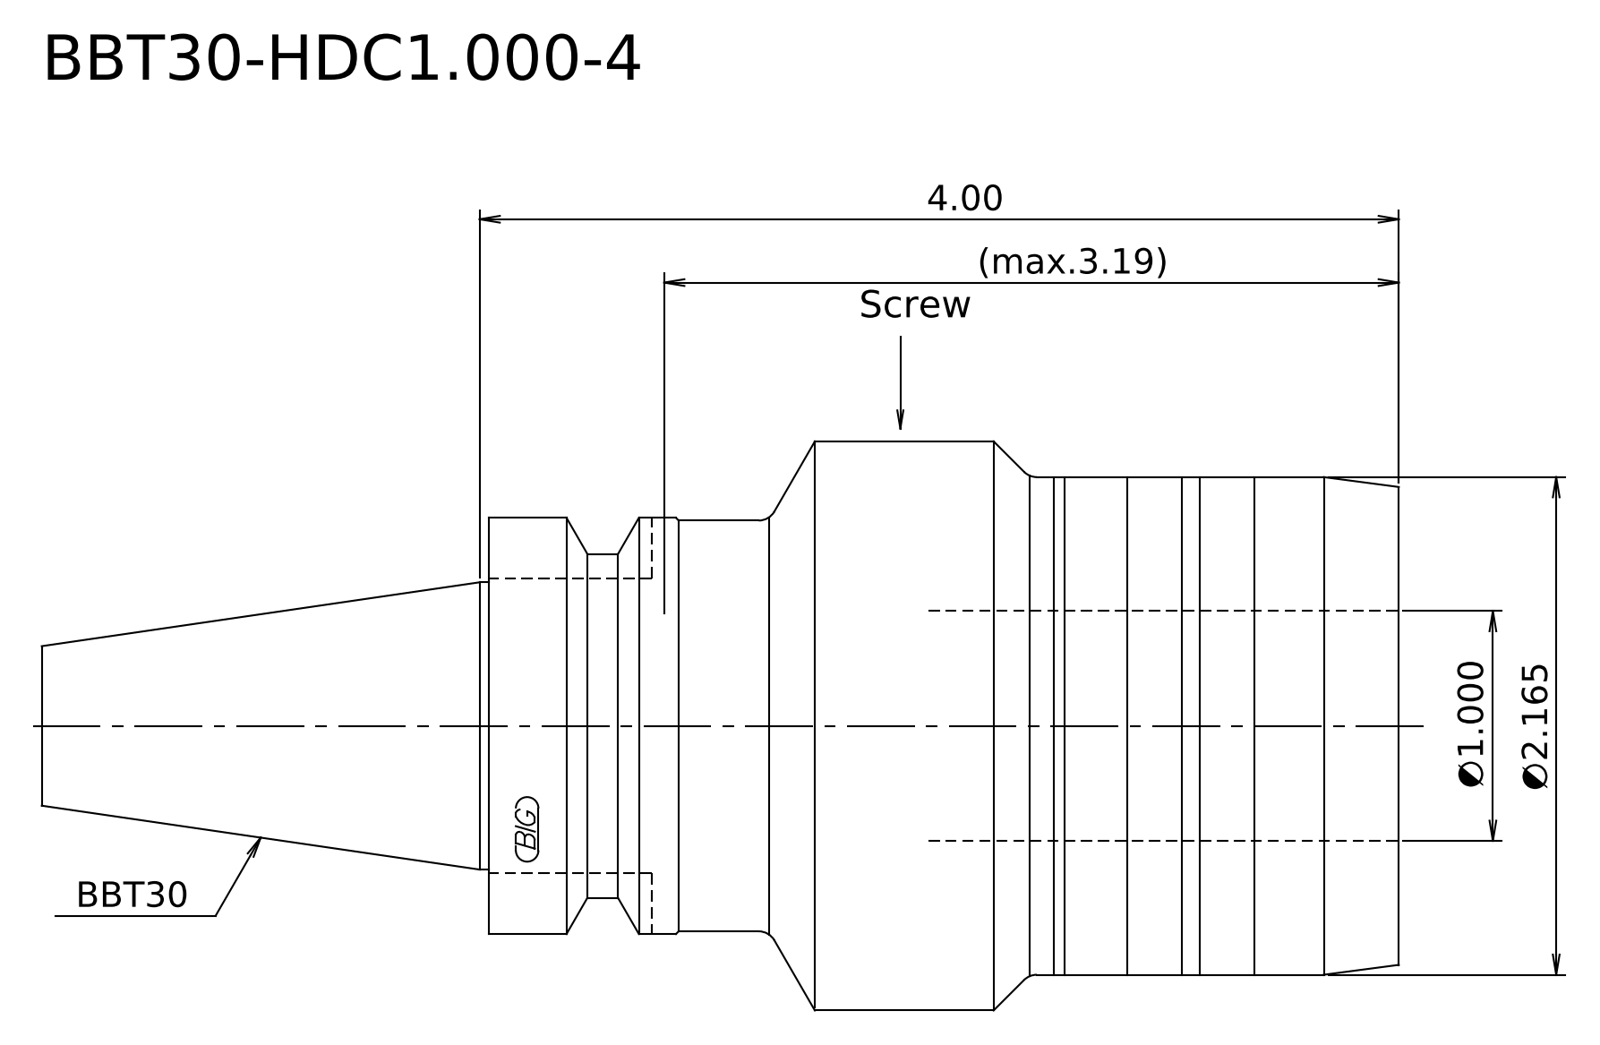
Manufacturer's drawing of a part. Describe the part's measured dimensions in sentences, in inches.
Its 3-D file was written by "Kubotek KeyCreator 2011 V10.0.2 (22737) (automotive_design)". It is 1 solid with 18 faces: 3 planar, 7 cylindrical and 8 other. Overall it measures 5.906 by 2.476 by 2.476 inches. Its volume is 15.43 cubic inches and its surface area 40.02 square inches. Round bosses or shafts: 1 of diameter 2.476, 1 of diameter 2.165, 1 of diameter 1.811, 1 of diameter 1.787, 1 of diameter 1.496, 1 of diameter 1.25. The main face-to-face distances are 3.961, 5.906, 1.945.
